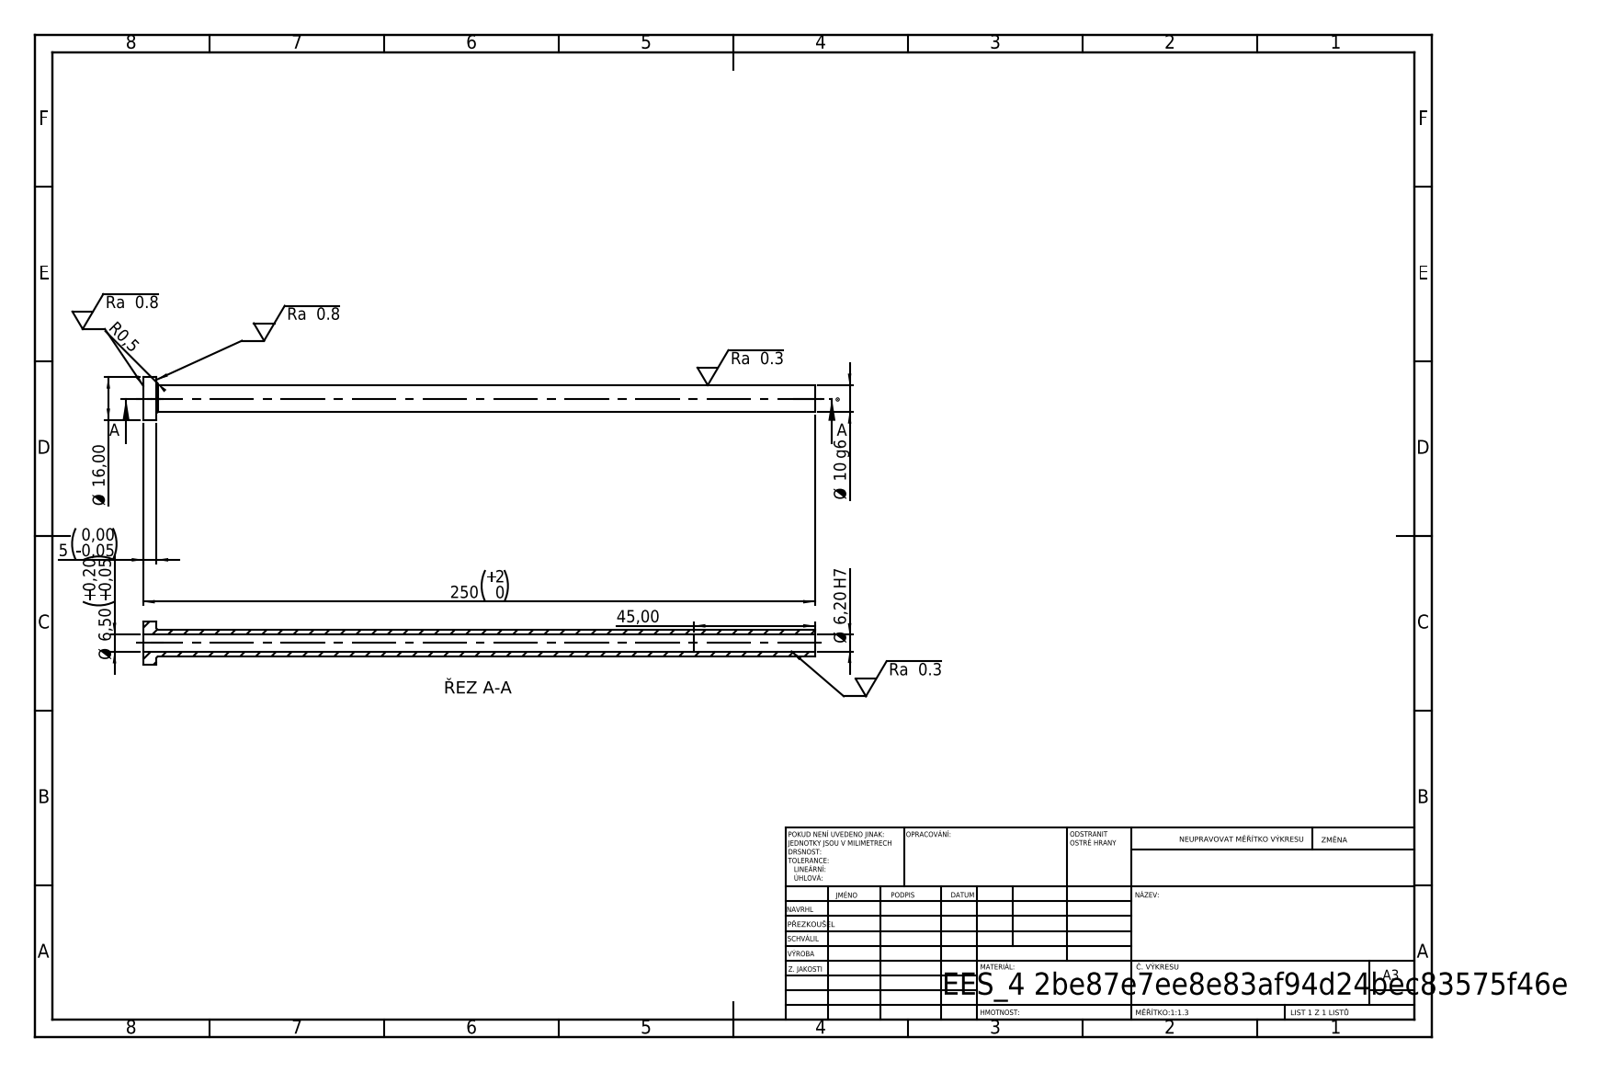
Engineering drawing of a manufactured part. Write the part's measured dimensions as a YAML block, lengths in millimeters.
step_written_by: "SolidWorks 2019 (CONFIG_CONTROL_DESIGN)"
units: millimeters
bodies: {solids: 1, faces: 14, planar: 4, cylindrical: 8, other: 2}
overall_size: [250, 16, 16]
volume: 12088
surface_area: 13346
round_holes:
  - {diameter: 6.2, count: 1}
  - {diameter: 6.5, count: 1}
round_bosses_or_shafts:
  - {diameter: 16, count: 1}
  - {diameter: 10, count: 1}
face_to_face_distances: [5, 250, 245, 205, 200, 45]
